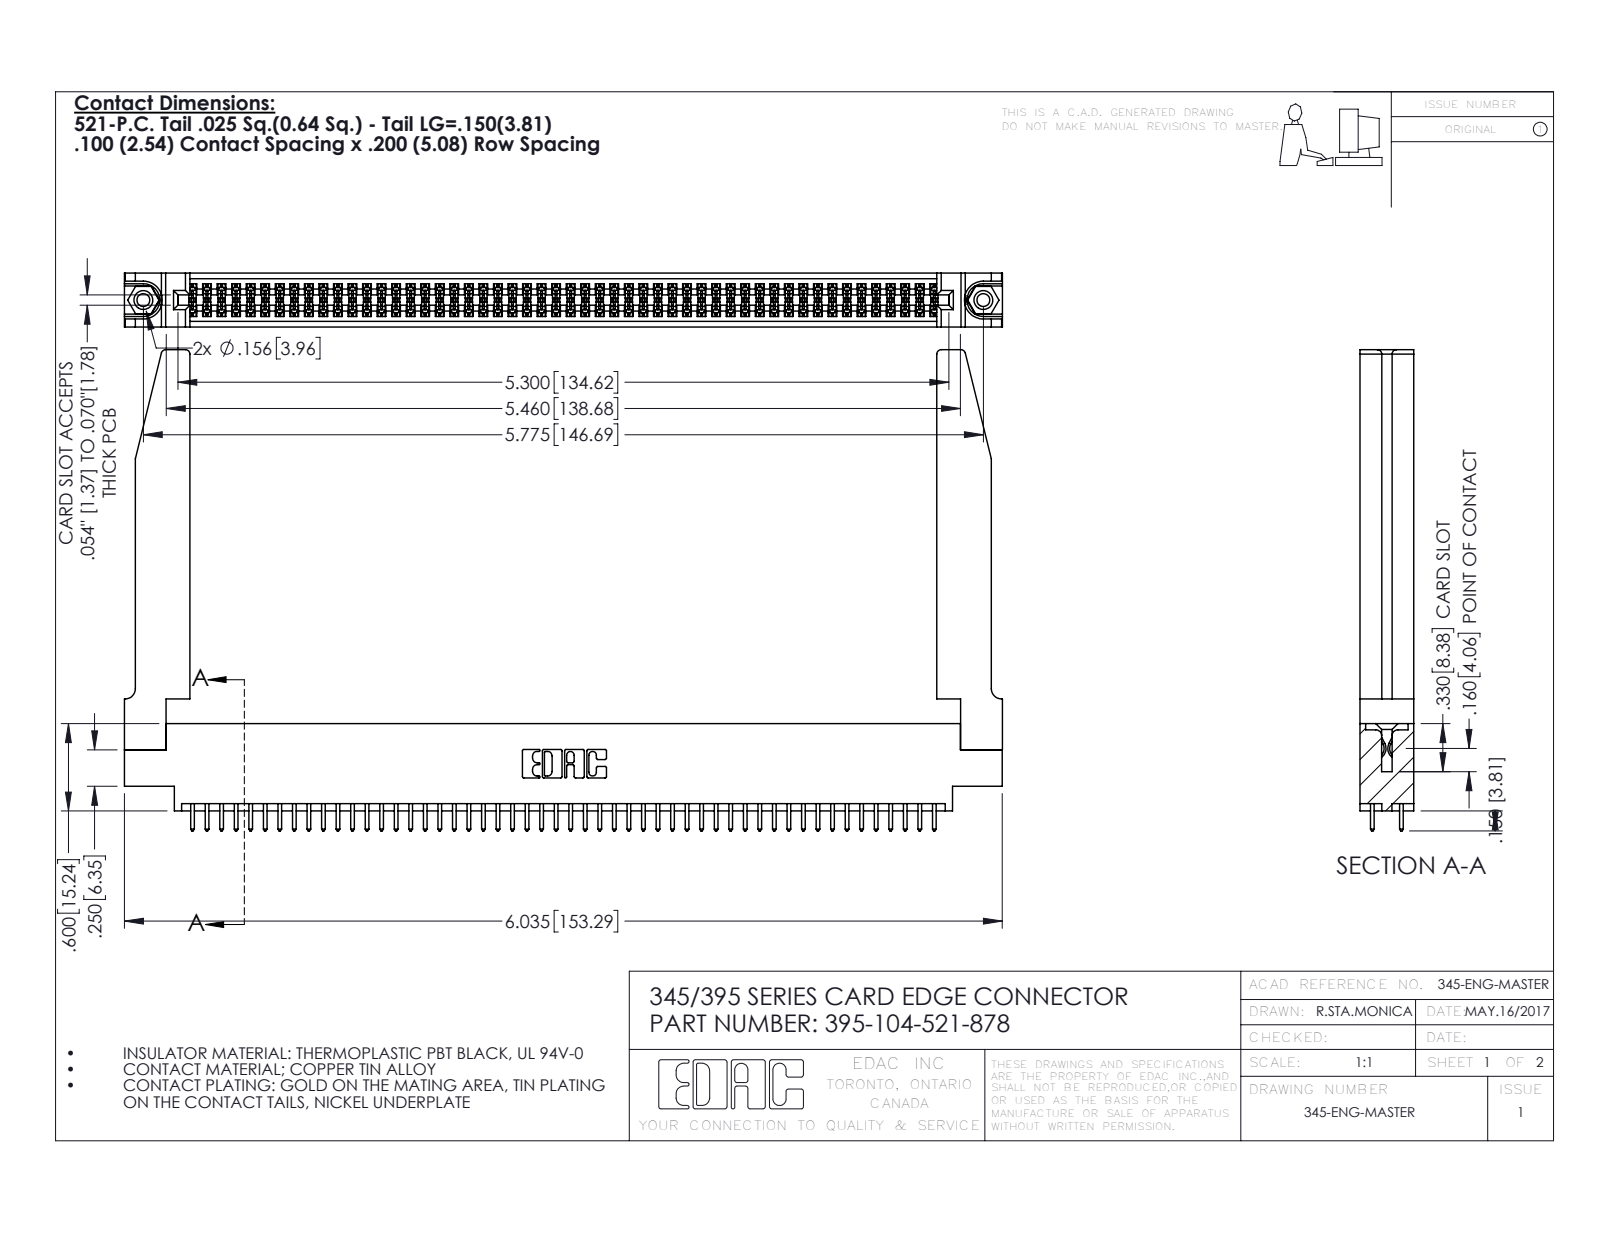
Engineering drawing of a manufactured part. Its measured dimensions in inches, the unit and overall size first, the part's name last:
Units: inches
Overall size (bounding box): 6.036 × 3.307 × 0.37
Round holes (diameter × count): ⌀0.089 ×2, ⌀0.125 ×2, ⌀0.156 ×2, ⌀0.064 ×1
Round bosses / shafts (diameter × count): ⌀0.155 ×2
Partial cylindrical surfaces — rounded edges, fillets, slot ends (radius × count): R0.006 ×156, R0.01 ×104, R0.01 ×22, R0.03 ×8, R0.007 ×6, R0.031 ×6, R0.026 ×3, R0.014 ×2
Main face-to-face distances: 0.072, 0.37, 0.298, 0.098, 0.272, 0.025, 0.2, 0.225, 0.175, 0.15
Hole centre spacings: 0.27, 5.539, 5.775
Volume: 1.379 in³ · Surface area: 44.67 in²
Bodies: 109 solids, 5564 faces (3658 planar, 1854 cylindrical, 52 other)
Part name (STEP PRODUCT): 395-104-521-878; 345-220-078_345-220-078; 345-292-001_345-293-121; 345 Part_0.170 Offset - 0.156 Dia-TH (+1 more)
STEP written by: SolidWorks 2016 (CONFIG_CONTROL_DESIGN)
